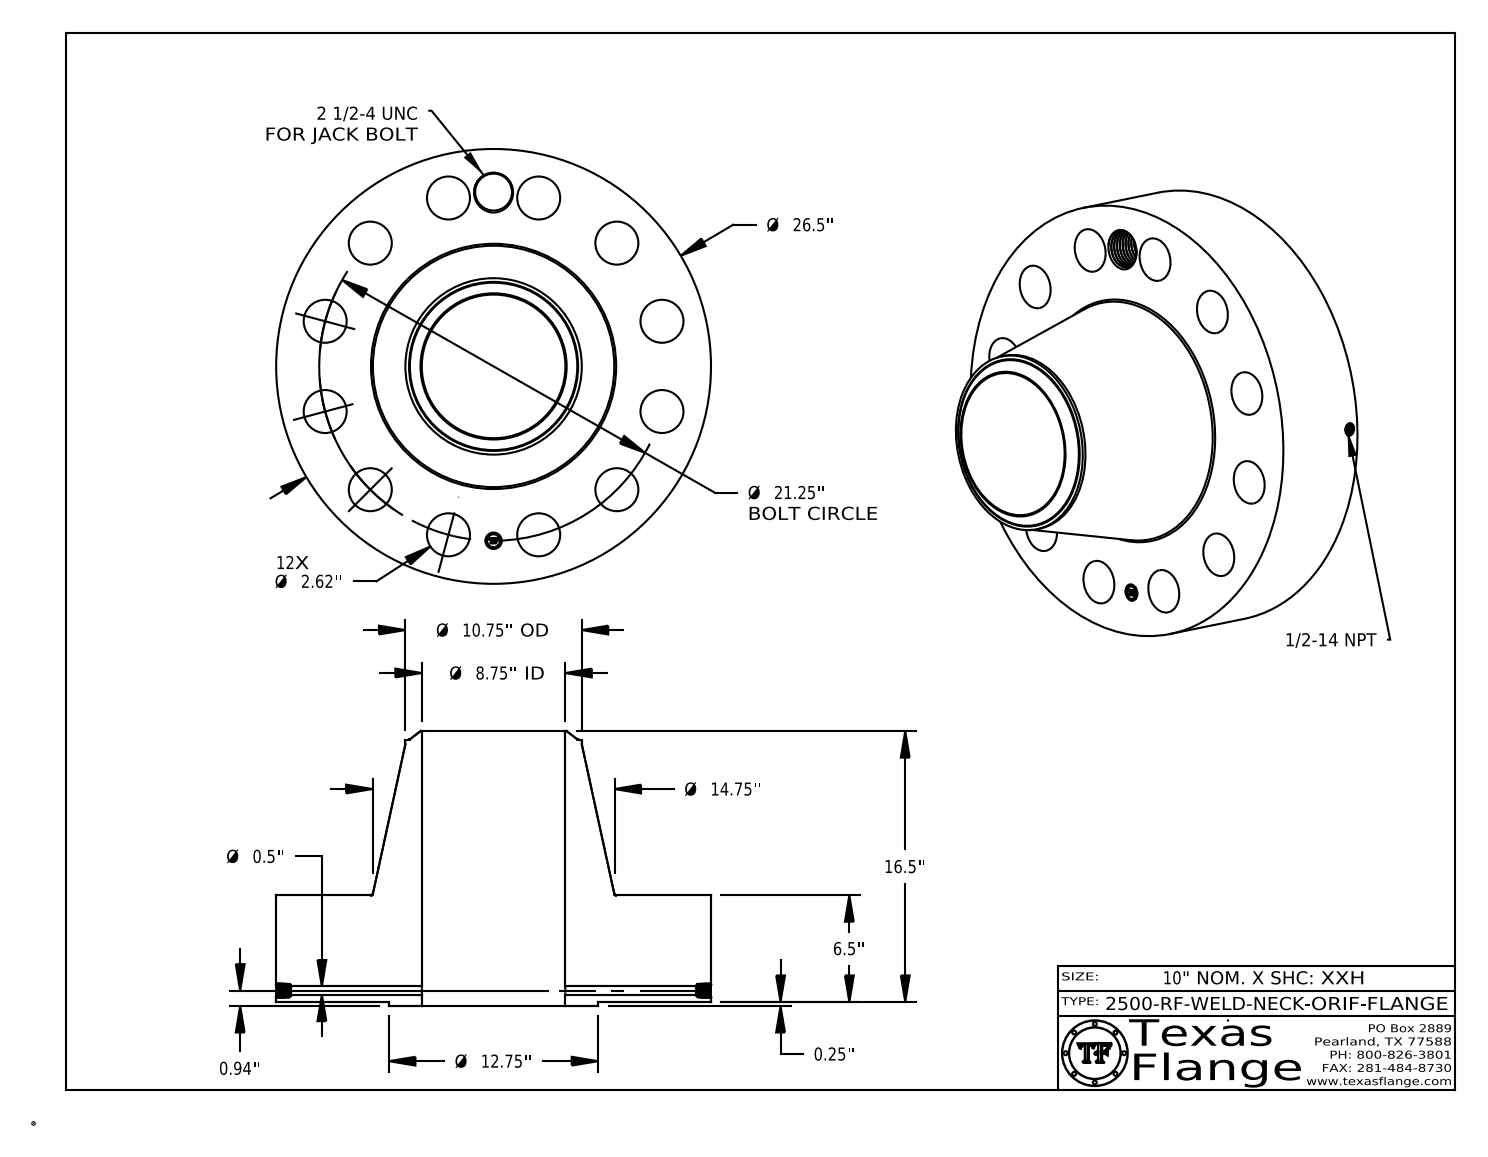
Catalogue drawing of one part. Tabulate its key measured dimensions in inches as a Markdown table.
| quantity | value |
| --- | --- |
| part name | 2500-RF-WELD-NECK |
| STEP written by | CATIA V5 STEP AP214 (AUTOMOTIVE_DESIGN) |
| units | inches |
| bodies | 1 solid, 847 faces (369 planar, 124 cylindrical, 354 other) |
| overall size | 26.5 × 26.5 × 16.75 |
| volume | 3 404 in³ |
| surface area | 2 907 in² |
| round holes (diameter × count) | 2.62 × 12, 0.5 × 1, 0.672 × 1, 1 × 1, 2.25 × 1, 8.75 × 1 |
| round bosses / shafts (diameter × count) | 0.061 × 8, 26.5 × 1, 12.75 × 1, 10.75 × 1, 0.788 × 1 |
| main face-to-face distances | 6.5, 0.25, 6.75, 16.75, 16.5, 10, 0.015, 6.735, 6.485, 10.015 |
| hole center spacings | 10.625, 5.5, 15.026, 18.403, 20.526, 10.625, 21.25, 2.774 |
